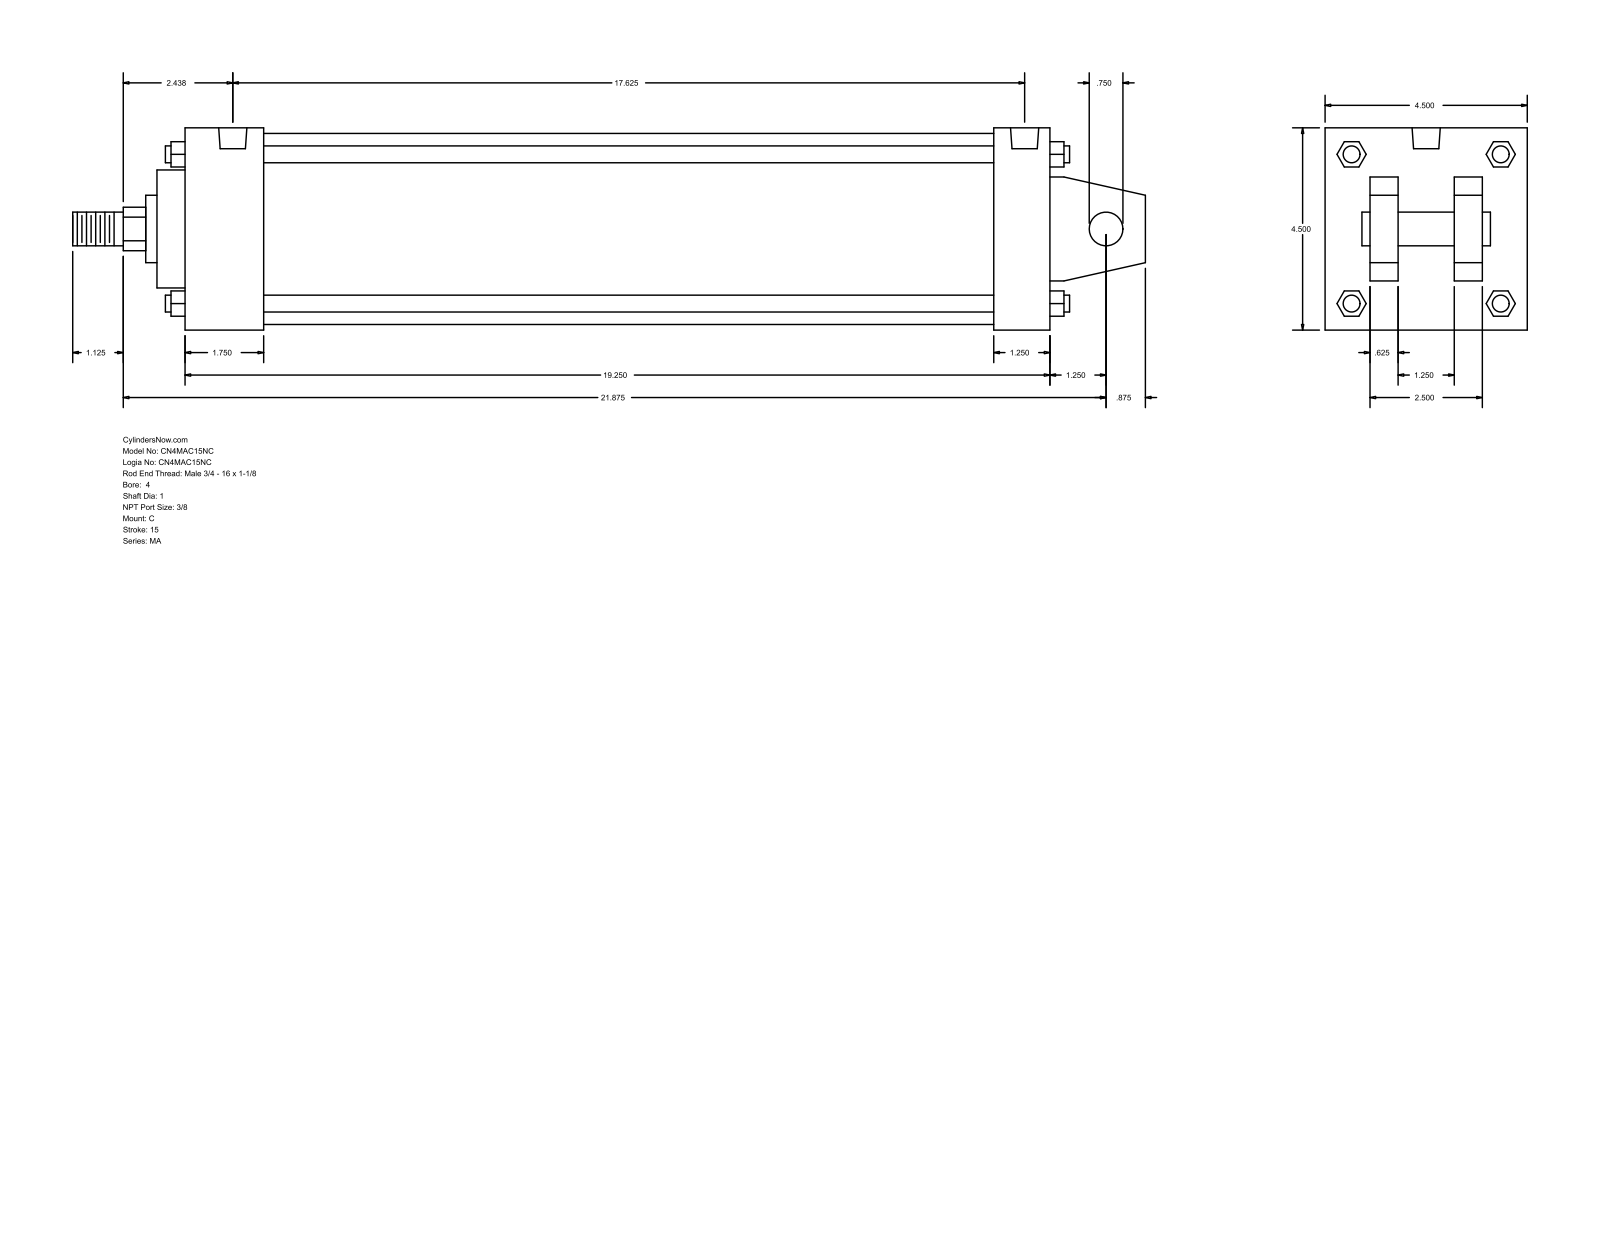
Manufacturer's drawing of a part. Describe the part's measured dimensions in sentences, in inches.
The part is named "MA_C__0400_1". Its 3-D file was written by "GSSL Pune (CONFIG_CONTROL_DESIGN)". It is 0 solids with 141 faces: 109 planar, 32 cylindrical and 0 other. Overall it measures 23.875 by 4.5 by 4.5 inches. Round holes: 4 of diameter 0.437, 2 of diameter 0.627. Round bosses or shafts: 4 of diameter 0.375, 2 of diameter 0.75, 1 of diameter 4.25, 1 of diameter 2.625, 1 of diameter 1.5, 1 of diameter 1. Partial cylindrical surfaces (rounded edges, fillets, slot ends): 1 of radius 0.484. The main face-to-face distances are 4.5, 19.25, 0.625, 1.25, 2.875, 1.625, 1, 3.5, 1.875, 18. The hole center spacings are 17.25, 0.187, 0.188, 17.437, 17.438, 17.625.
